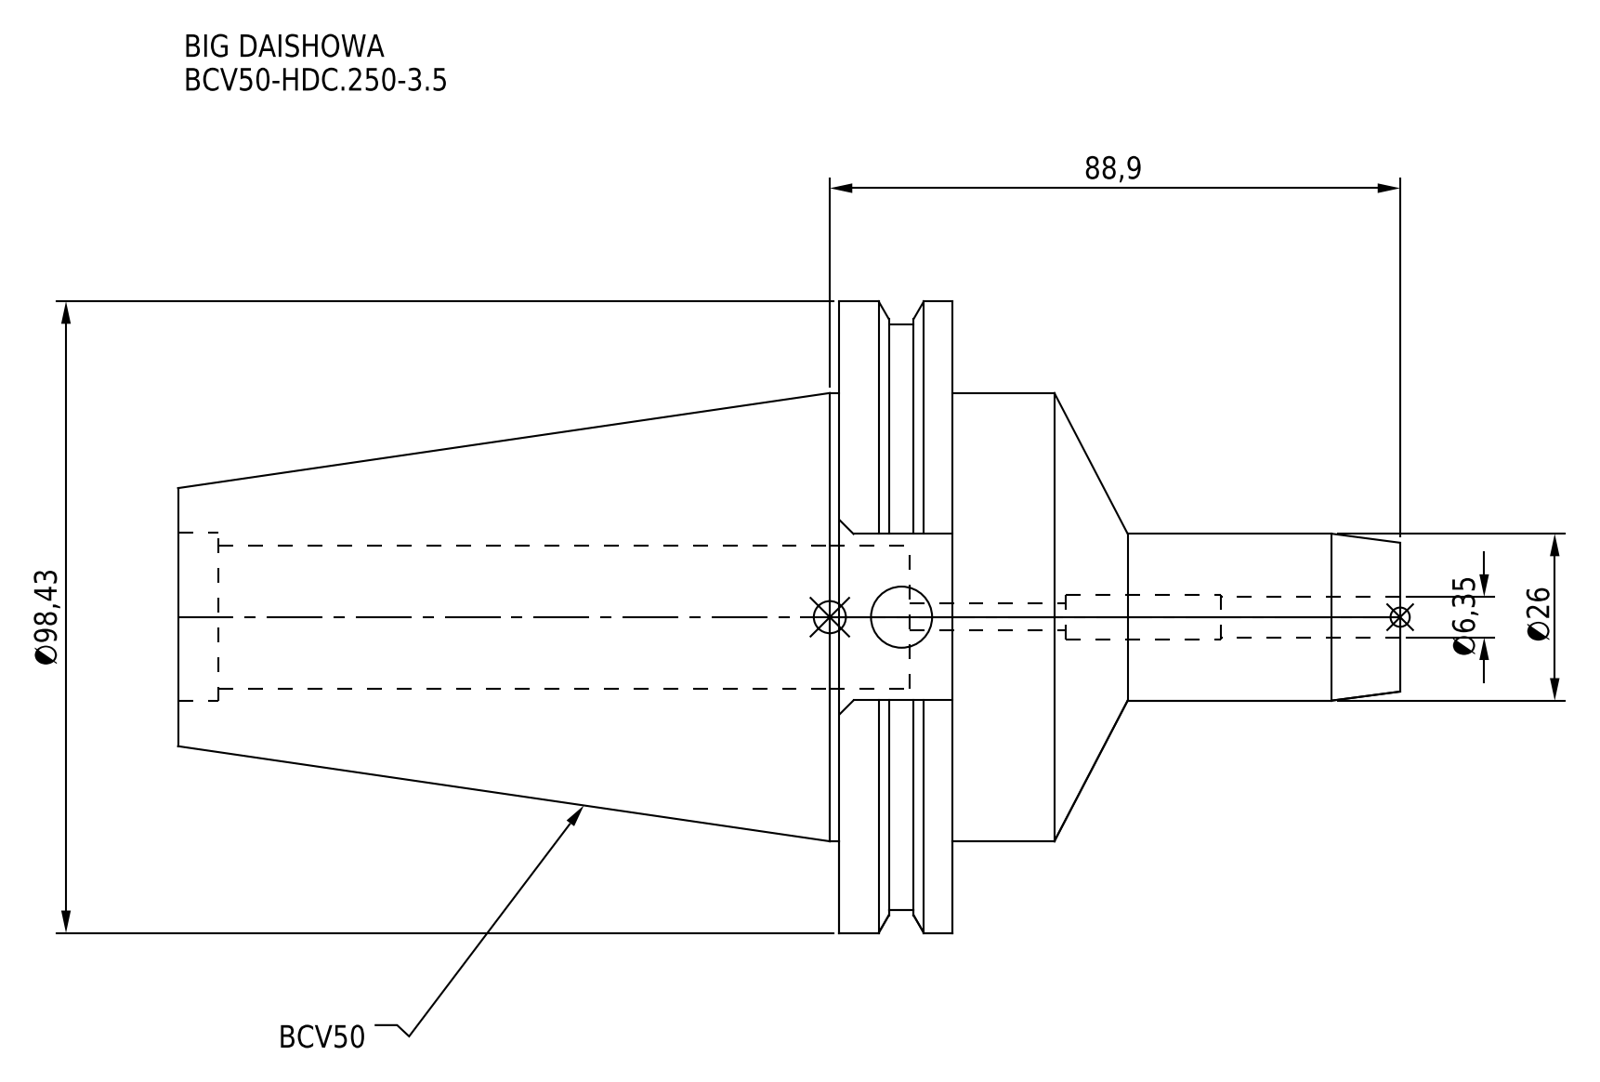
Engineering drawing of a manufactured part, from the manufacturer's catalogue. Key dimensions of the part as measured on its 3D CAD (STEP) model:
Part name (STEP PRODUCT): BCV50-HDC_250-3_5
STEP written by: CREO PARAMETRIC BY PTC INC, 2016380 (AUTOMOTIVE_DESIGN)
Units: millimetres
Bodies: 1 solid, 59 faces (23 planar, 26 cylindrical, 10 other)
Overall size (bounding box): 190.5 × 98.42 × 94.95
Volume: 428 639 mm³ · Surface area: 53 289 mm²
Round holes (diameter × count): ⌀4.2 ×1, ⌀6.35 ×1, ⌀6.9 ×1, ⌀9.53 ×1, ⌀22.3 ×1, ⌀26.23 ×1
Round bosses / shafts (diameter × count): ⌀98.42 ×1, ⌀91.29 ×1, ⌀69.85 ×1, ⌀26 ×1
Main face-to-face distances: 17.55, 120.65, 103.1, 69.85, 87.4, 190.5, 72.95, 76.5, 6.65, 10.9
